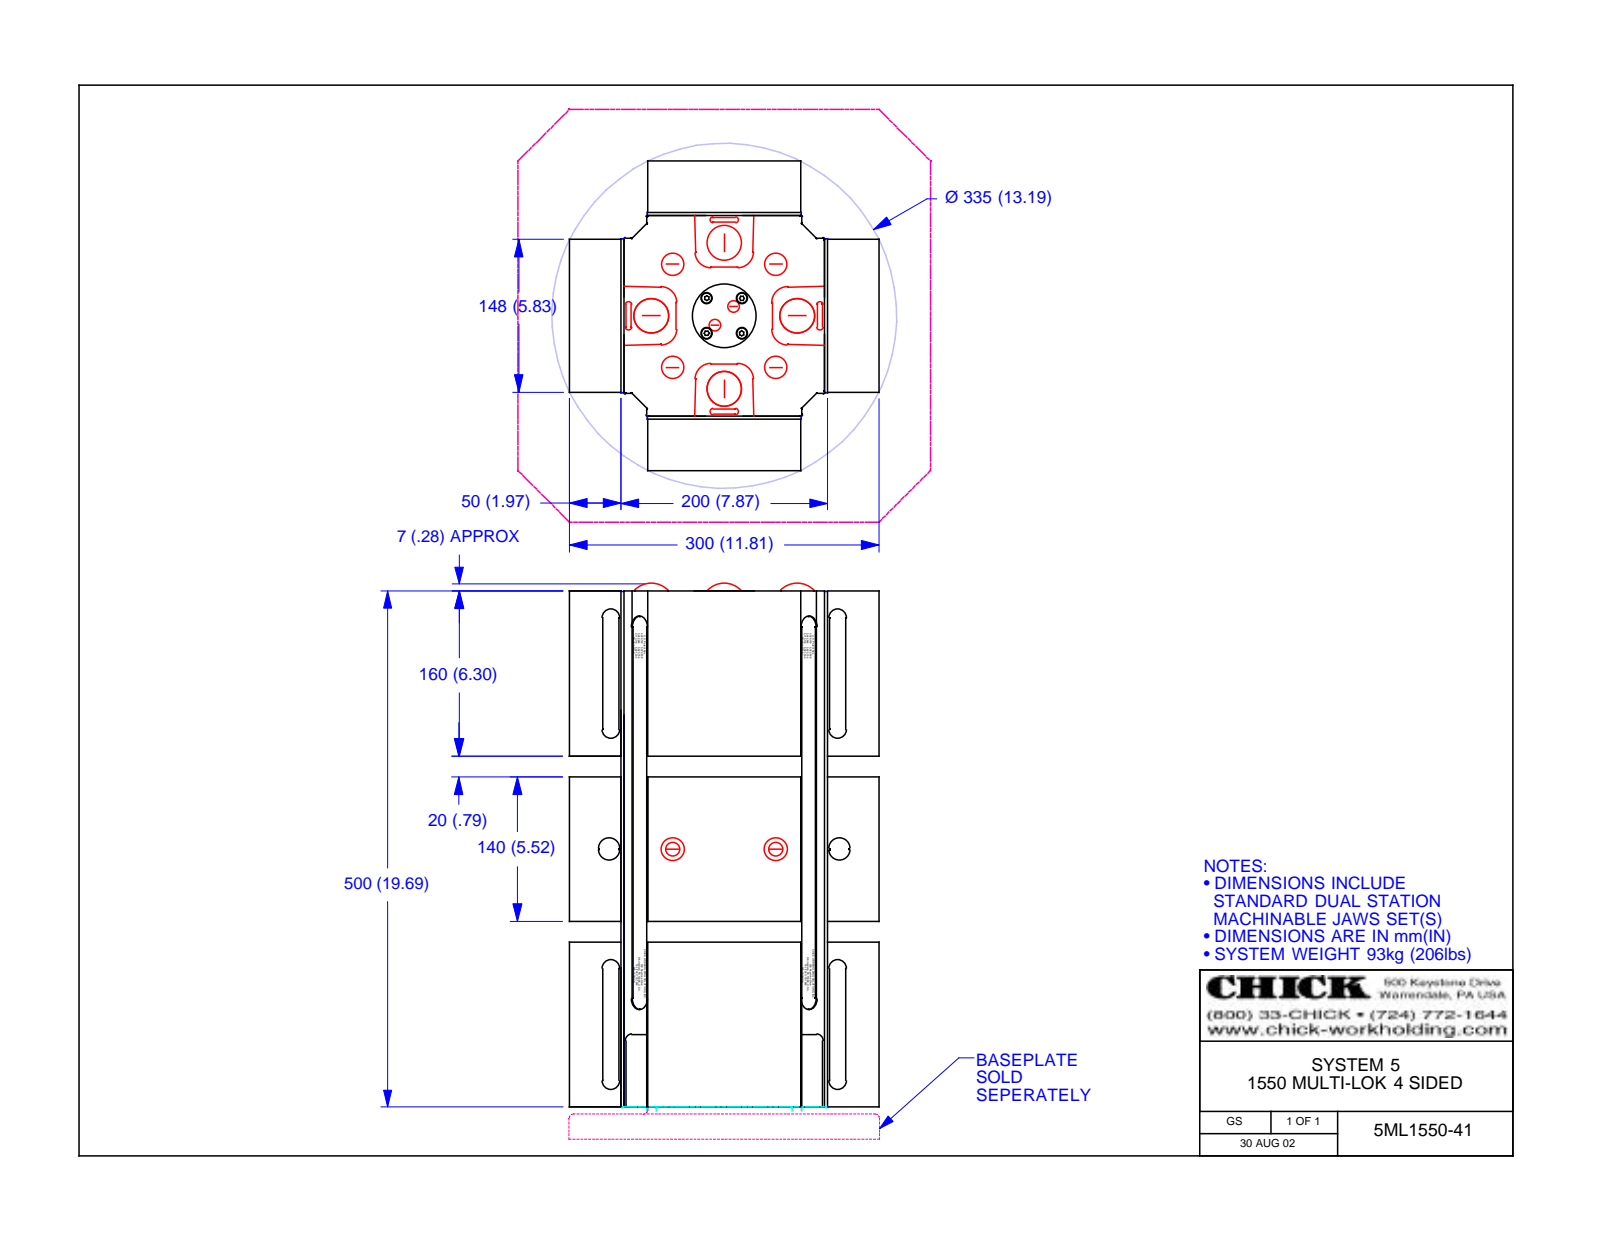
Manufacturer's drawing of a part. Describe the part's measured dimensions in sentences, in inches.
The part is named "5ML1550-41; 5CLM1550-41; 5CP1550-ST; 5DS1550-15-50 (+2 more)". Its 3-D file was written by "Autodesk Inventor 2013 (AUTOMOTIVE_DESIGN)". It is 17 solids with 6609 faces: 5320 planar, 464 cylindrical and 825 other. Overall it measures 19.969 by 11.811 by 11.811 inches. Its volume is 1 720 cubic inches and its surface area 3 433 square inches. Round holes: 16 of diameter 0.669, 12 of diameter 0.406, 12 of diameter 0.433, 12 of diameter 0.715, 12 of diameter 0.787, 12 of diameter 1.062, 8 of diameter 0.341, 8 of diameter 0.398, 8 of diameter 0.413, 8 of diameter 0.709, 6 of diameter 0.394, 4 of diameter 0.16. Round bosses or shafts: 8 of diameter 0.335, 4 of diameter 0.302, 4 of diameter 0.187. Partial cylindrical surfaces (rounded edges, fillets, slot ends): 112 of radius 0.079, 16 of radius 0.016, 16 of radius 0.047, 16 of radius 0.626, 8 of radius 0.065, 8 of radius 0.111, 8 of radius 0.118, 8 of radius 0.404. The main face-to-face distances are 0.118, 7.756, 1.969, 7.874, 9.843, 2.087, 9.724, 7.638, 4.489, 5.236. The hole center spacings are 6.89, 3.937, 9.055, 0.016, 2.165, 7.935, 15.945, 7.928.
